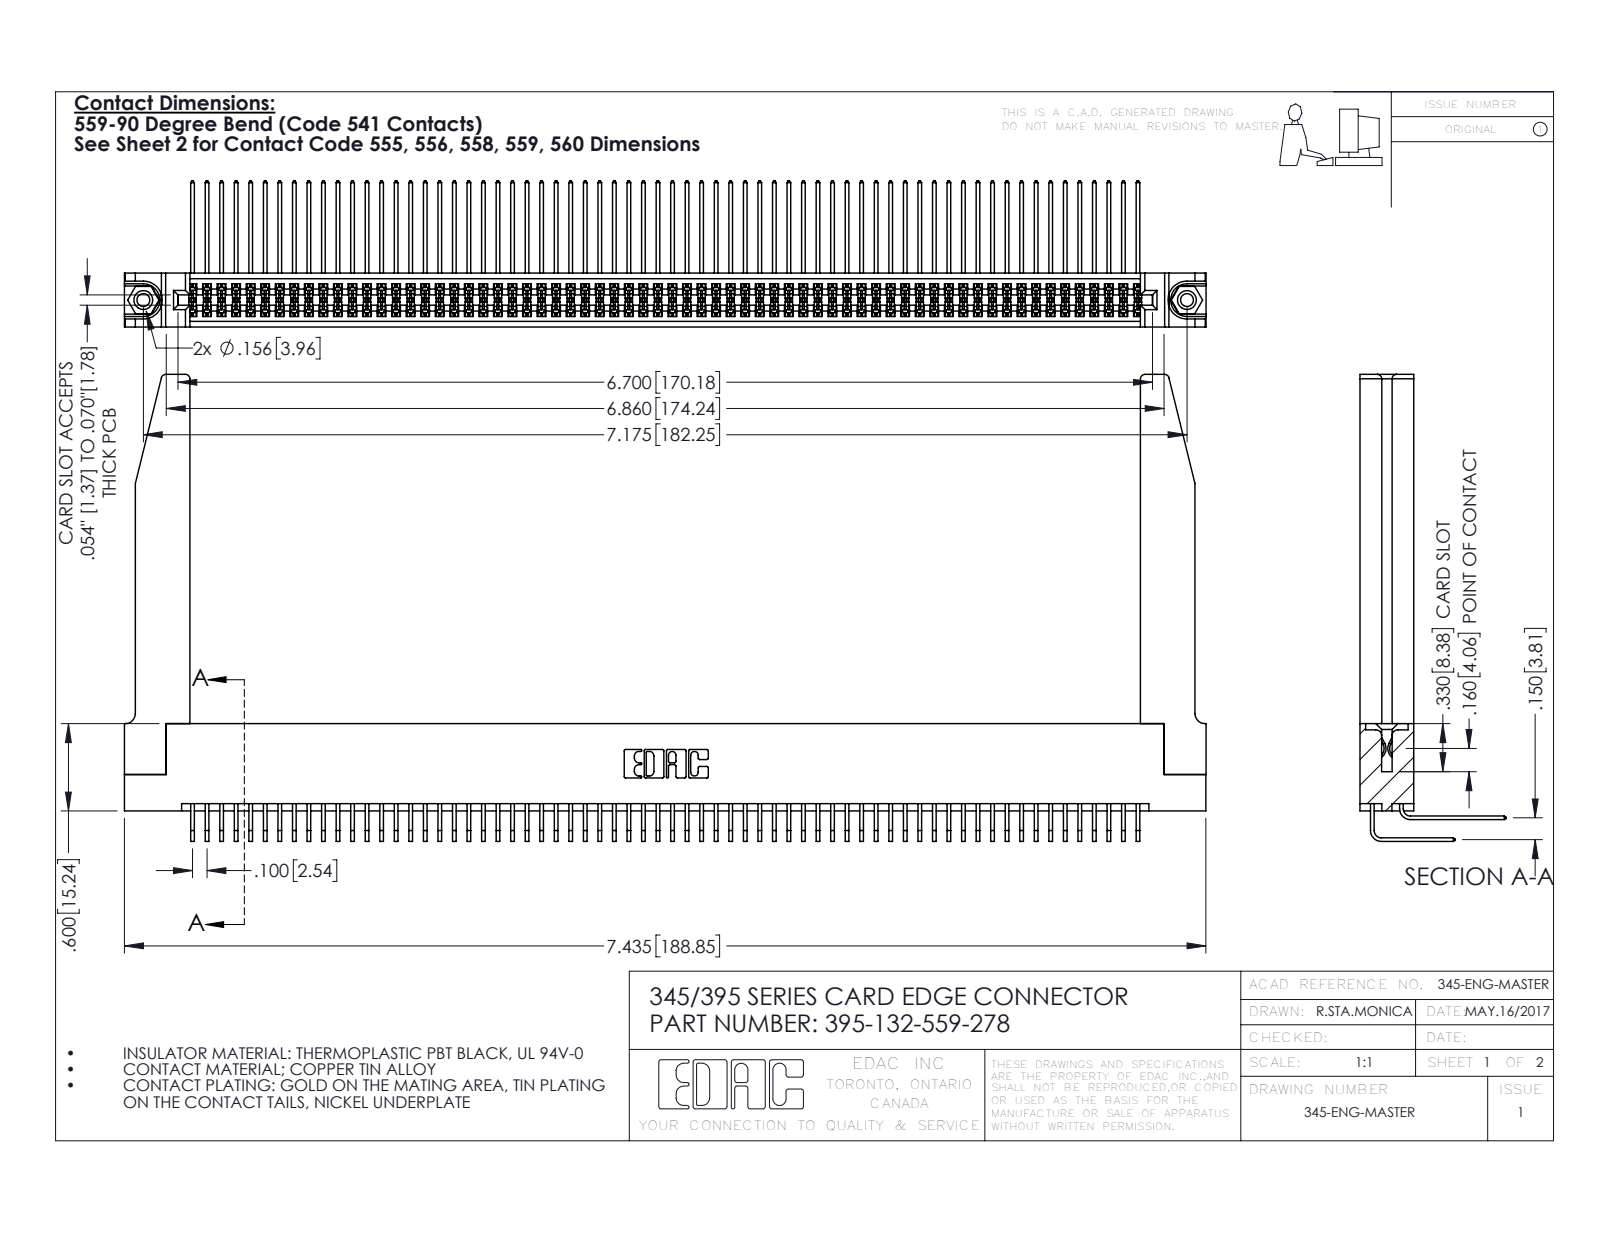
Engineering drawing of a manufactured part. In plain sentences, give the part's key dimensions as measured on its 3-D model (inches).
The part is named "395-132-559-278; 345-292-001_558 559 Tail - 1; 345-220-078_345-220-078; 345-292-001_559 Tail - 2 (+2 more)". Its 3-D file was written by "SolidWorks 2016 (CONFIG_CONTROL_DESIGN)". It is 137 solids with 7224 faces: 4842 planar, 2330 cylindrical and 52 other. Overall it measures 7.436 by 3.209 by 1.005 inches. Its volume is 1.654 cubic inches and its surface area 61.16 square inches. Round holes: 2 of diameter 0.089, 2 of diameter 0.125, 2 of diameter 0.156, 1 of diameter 0.064. Round bosses or shafts: 2 of diameter 0.155. Partial cylindrical surfaces (rounded edges, fillets, slot ends): 199 of radius 0.006, 22 of radius 0.01, 8 of radius 0.03, 6 of radius 0.007, 6 of radius 0.031, 3 of radius 0.026, 2 of radius 0.014, 2 of radius 0.019. The main face-to-face distances are 0.072, 0.298, 0.37, 0.2, 0.098, 0.272, 0.025, 0.225, 0.175, 0.15. The hole center spacings are 0.27, 6.939, 7.175.
